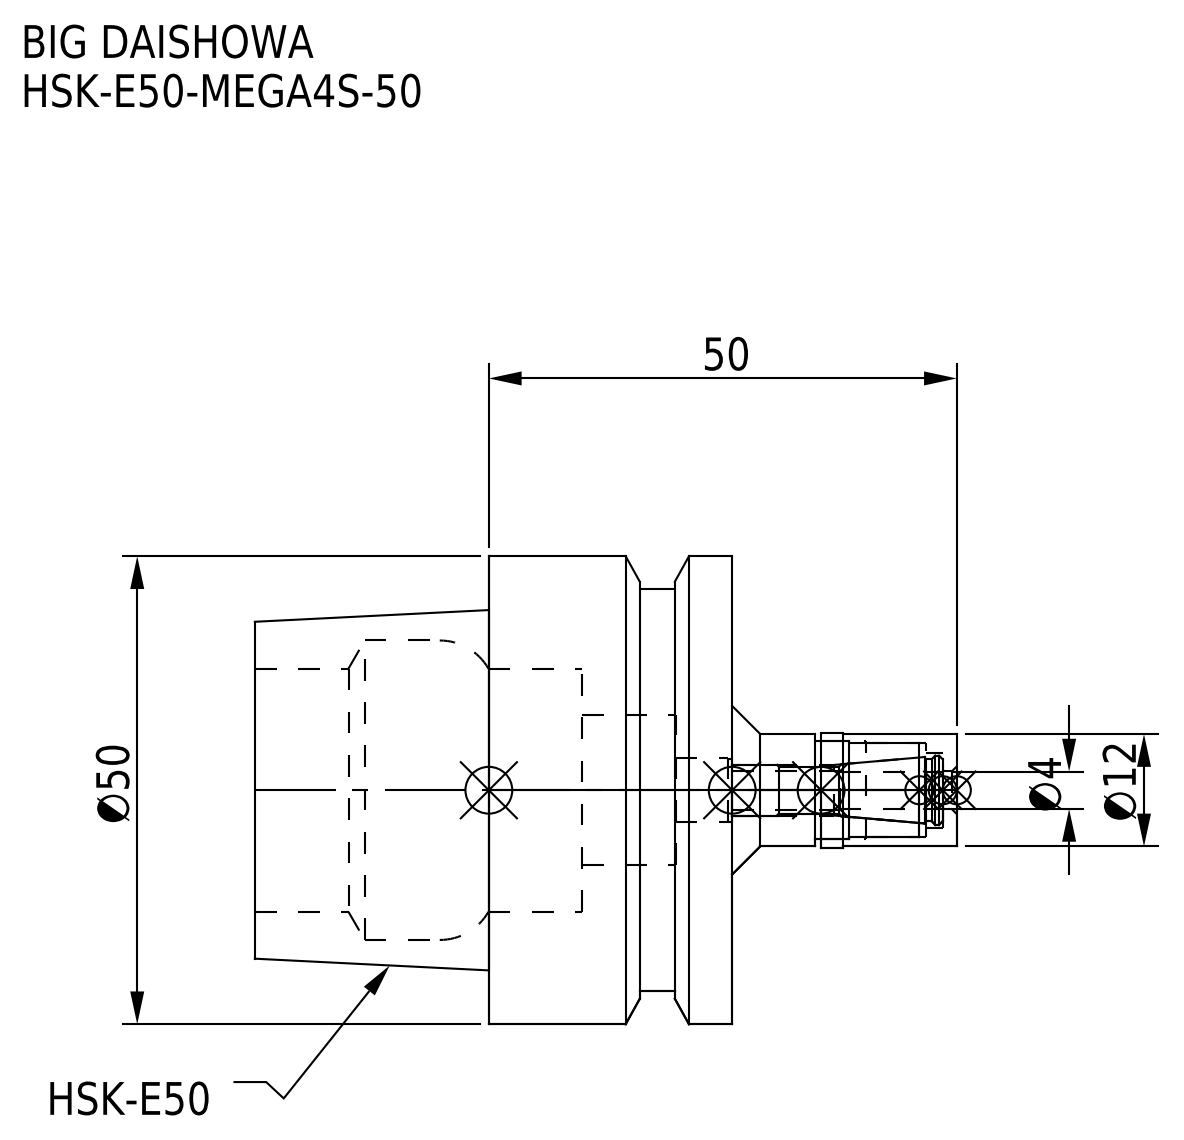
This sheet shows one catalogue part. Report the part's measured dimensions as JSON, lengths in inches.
{"part_name": "MGN4S_1.stp; HSK-E50-MEGA4S-50_1.stp; HSK-E50-MEGA4S-50-040-FreeParts; HSK-E50-MEGA4S-50-040.stp (+3 more)", "step_written_by": "SolidWorks 2019 (CONFIG_CONTROL_DESIGN)", "units": "inches", "bodies": {"solids": 2, "faces": 74, "planar": 18, "cylindrical": 40, "other": 16}, "overall_size": [2.953, 1.969, 1.969], "volume_in3": 3.281, "surface_area_in2": 27.08, "round_holes": [[0.161, 1], [0.213, 1], [0.264, 1], [0.268, 1], [0.315, 1], [0.394, 1], [0.413, 1], [0.63, 1], [1.024, 1], [1.26, 1]], "round_bosses_or_shafts": [[1.969, 1], [1.693, 1], [0.484, 1], [0.472, 1]], "face_to_face_distances": [1.024, 2.008, 0.984, 0.632, 0.392, 1.376, 0.394, 0.238, 0.785, 1.77]}
